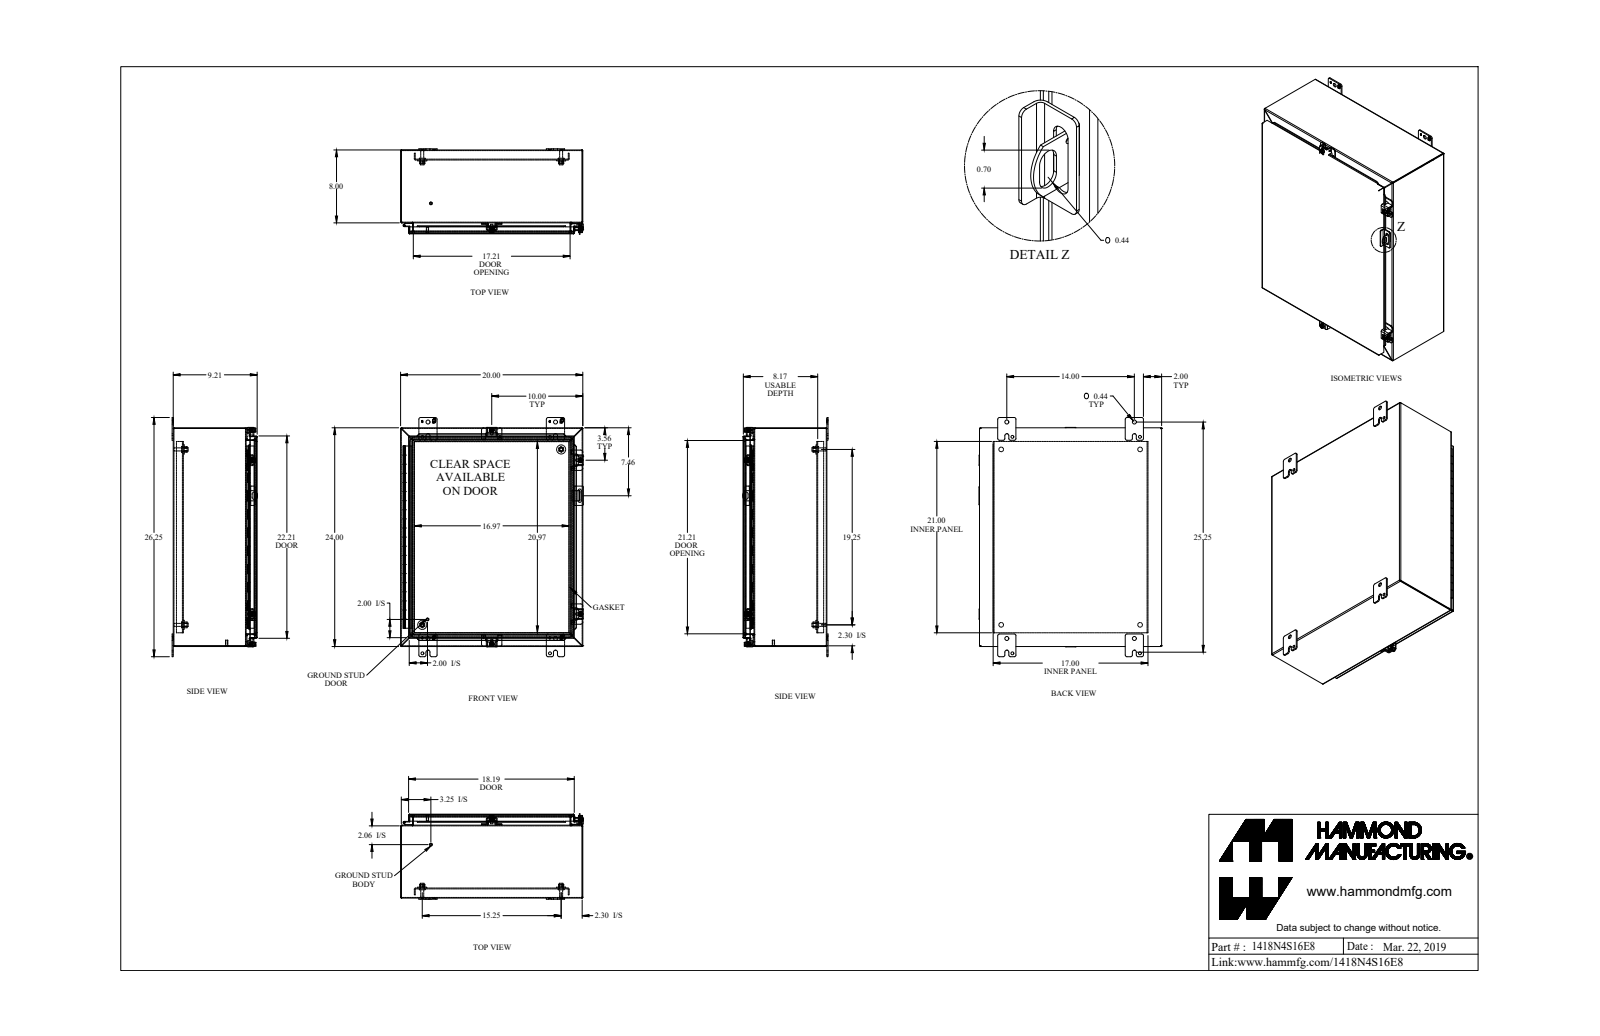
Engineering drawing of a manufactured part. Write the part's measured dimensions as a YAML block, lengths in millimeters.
part_name: "1418N4S16E8_Default"
step_written_by: "SolidWorks 2019 (CONFIG_CONTROL_DESIGN)"
units: millimeters
bodies: {solids: 39, faces: 1374, planar: 746, cylindrical: 494, other: 134}
overall_size: [666.8, 509.6, 238.1]
volume: 3020000
surface_area: 3135000
round_holes:
  - {diameter: 5.4, count: 4}
  - {diameter: 8, count: 4}
  - {diameter: 9.5, count: 4}
  - {diameter: 11.1, count: 4}
  - {diameter: 12.7, count: 4}
  - {diameter: 6.7, count: 2}
  - {diameter: 6.7, count: 2}
  - {diameter: 7.8, count: 2}
  - {diameter: 11.3, count: 2}
  - {diameter: 2.8, count: 1}
  - {diameter: 3.2, count: 1}
round_bosses_or_shafts:
  - {diameter: 16.5, count: 4}
  - {diameter: 12.7, count: 4}
  - {diameter: 9.9, count: 4}
  - {diameter: 9.5, count: 4}
  - {diameter: 8.4, count: 4}
  - {diameter: 6.2, count: 4}
  - {diameter: 25.4, count: 2}
  - {diameter: 8, count: 2}
partial_cylinders:
  - {radius: 4.8, count: 26}
  - {radius: 0.9, count: 24}
  - {radius: 2.7, count: 24}
  - {radius: 1.2, count: 21}
  - {radius: 3.6, count: 21}
  - {radius: 6.4, count: 20}
  - {radius: 3.2, count: 12}
  - {radius: 1.1, count: 8}
face_to_face_distances: [1.8, 230.3, 232.1, 1.8, 232.1, 233.9, 23.8, 2.4, 25.6, 506.2]
hole_center_spacings: [201.1, 576.4, 355.6, 623.8, 44.1, 61.8, 373.4, 387.4]
